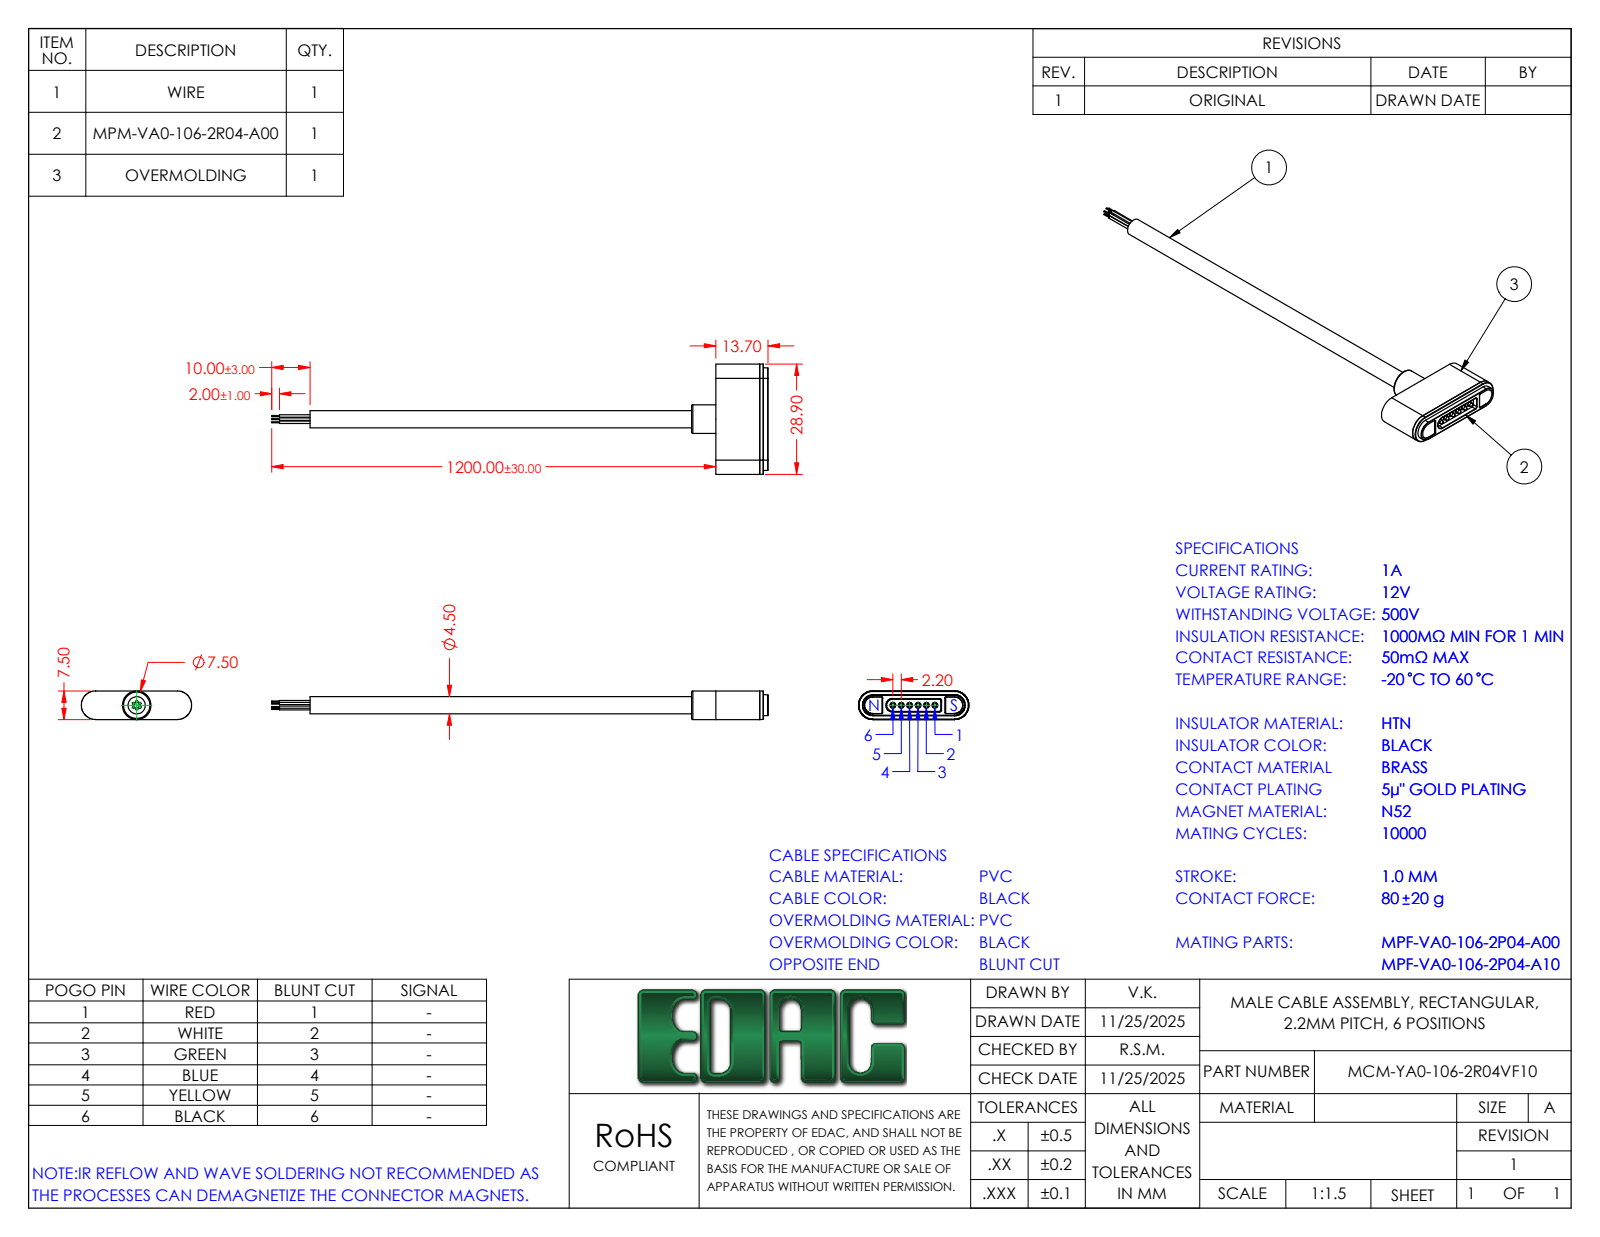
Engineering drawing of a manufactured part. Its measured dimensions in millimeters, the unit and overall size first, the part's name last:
Units: millimetres
Overall size (bounding box): 130.15 × 28.9 × 7.5
Round holes (diameter × count): ⌀1.5 ×6
Round bosses / shafts (diameter × count): ⌀1 ×6, ⌀0.6 ×6, ⌀0.3 ×6, ⌀7.5 ×1, ⌀4.5 ×1
Partial cylindrical surfaces — rounded edges, fillets, slot ends (radius × count): R0.1 ×8, R0.5 ×2, R2.2 ×2, R3.75 ×2
Main face-to-face distances: 7.5, 12.65, 11.65, 1, 1.55, 5.95, 13.85, 2.2, 1.2, 0.96
Hole centre spacings: 2.2, 4.4, 6.6, 8.8, 11
Bodies: 0 solids, 147 faces (39 planar, 68 cylindrical, 40 other)
Part name (STEP PRODUCT): MCM-YA0-106-2R04VF10
STEP written by: SolidWorks 2023 (CONFIG_CONTROL_DESIGN)
